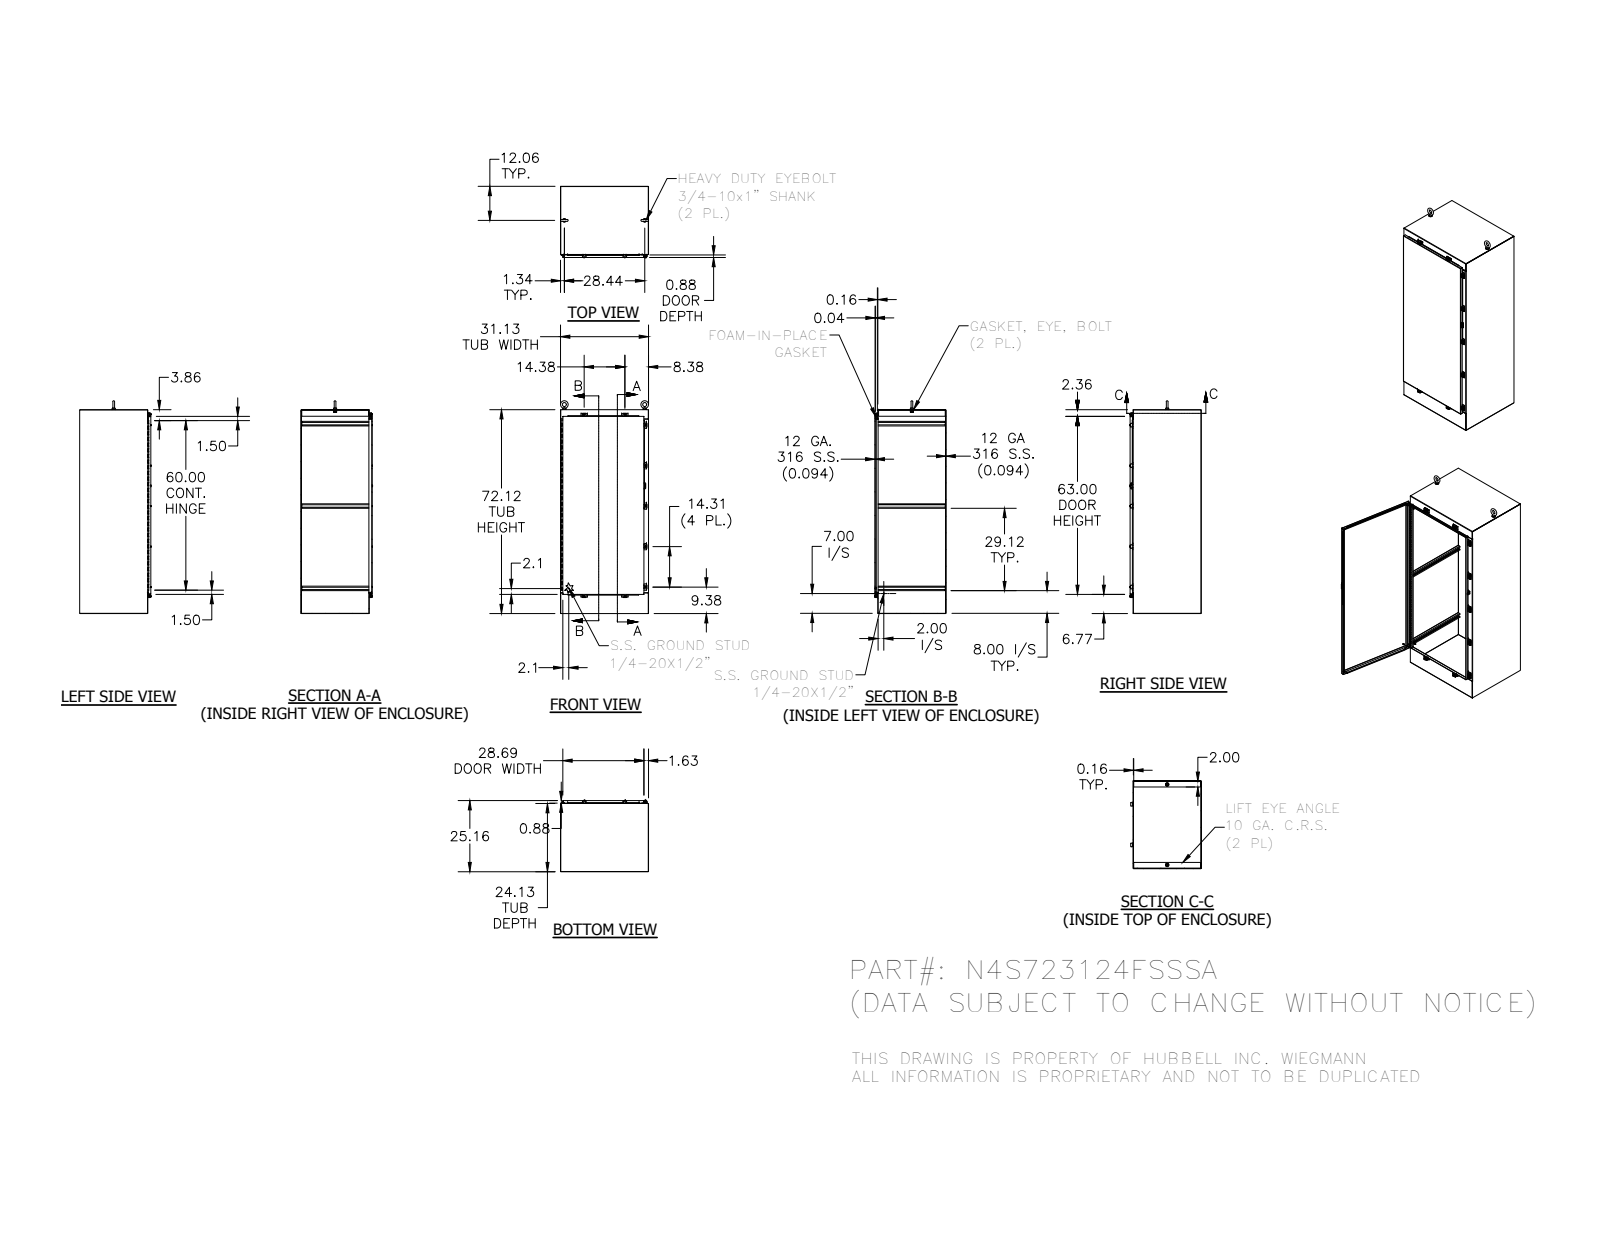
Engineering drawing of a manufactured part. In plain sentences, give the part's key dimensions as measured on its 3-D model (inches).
The part is named "N4S31.13FSSSADS_1; N4S723124FSSSA; HFW3025_1; 30824-3_1 (+8 more)". Its 3-D file was written by "SolidWorks 2014 (AUTOMOTIVE_DESIGN)". It is 78 solids with 3000 faces: 1210 planar, 1210 cylindrical and 580 other. Overall it measures 75.248 by 31.125 by 25.355 inches. Its volume is 1 113 cubic inches and its surface area 22 932 square inches. Round holes: 9 of diameter 0.211, 9 of diameter 0.281, 9 of diameter 0.3, 3 of diameter 0.11, 2 of diameter 0.642, 2 of diameter 0.813, 1 of diameter 0.125, 1 of diameter 0.156, 1 of diameter 0.5. Round bosses or shafts: 12 of diameter 0.25, 9 of diameter 0.52, 9 of diameter 0.5, 9 of diameter 0.35, 2 of diameter 1.25, 2 of diameter 1.12, 2 of diameter 0.75, 2 of diameter 0.337. Partial cylindrical surfaces (rounded edges, fillets, slot ends): 107 of radius 0.03, 43 of radius 0.125, 22 of radius 0.062, 21 of radius 0.25, 19 of radius 0.031, 18 of radius 0.019, 18 of radius 0.053, 18 of radius 0.086. The main face-to-face distances are 0.094, 25.067, 31.031, 24.973, 25.161, 30.938, 31.125, 72.031, 24.031, 1.035. The hole center spacings are 14.313, 28.626, 0.789, 14.38, 42.939, 64.375, 65.961, 0.449.
